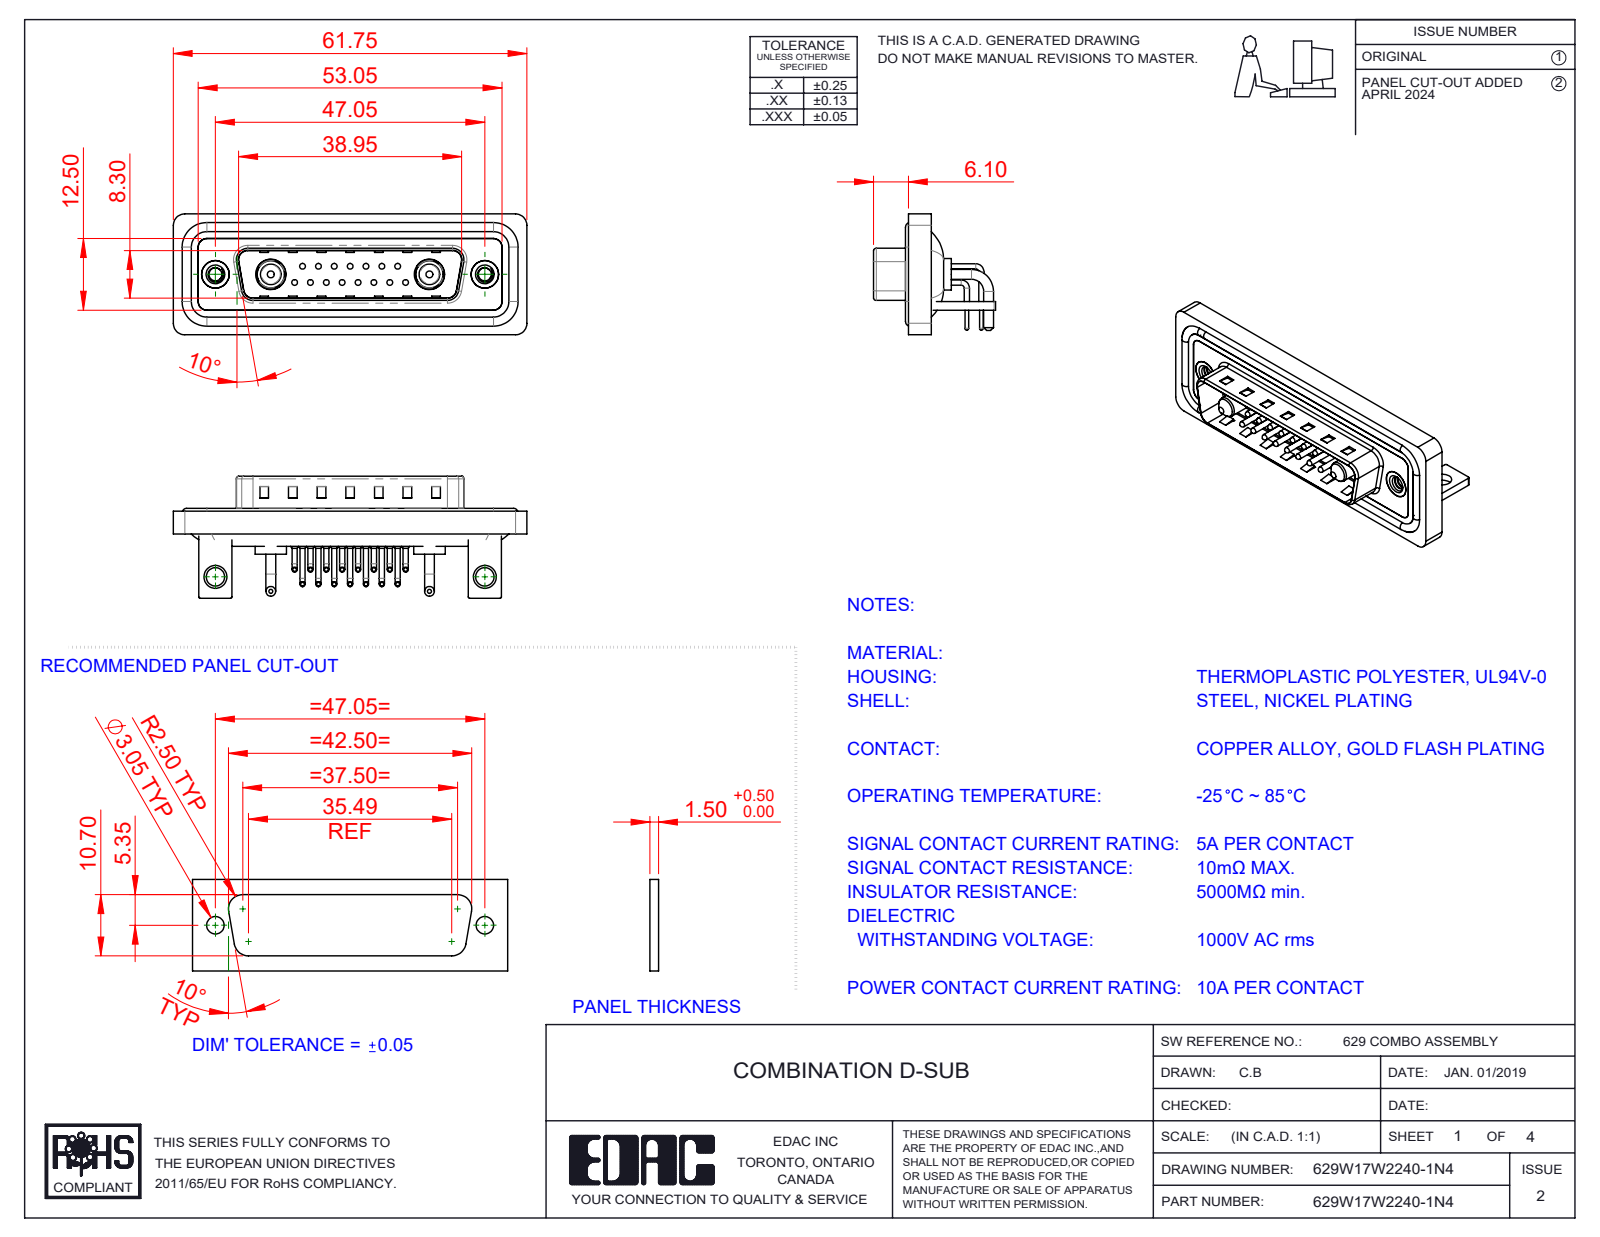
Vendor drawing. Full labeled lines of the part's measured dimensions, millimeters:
Part name (STEP PRODUCT): 629Combo Waterproof Housing_25 Contacts; 629W17W2140-1N4; 629Combo Contact Row 2; Power Pin_10A RA (+6 more)
STEP written by: SolidWorks 2023 (CONFIG_CONTROL_DESIGN)
Units: millimetres
Bodies: 28 solids, 2259 faces (1209 planar, 788 cylindrical, 262 other)
Overall size (bounding box): 61.75 × 21.3 × 21.1
Volume: 7 674 mm³ · Surface area: 13 086 mm²
Round holes (diameter × count): ⌀0.75 ×15, ⌀1.6 ×15, ⌀2 ×15, ⌀2.26 ×2, ⌀3.2 ×2, ⌀4 ×2, ⌀4.8 ×2, ⌀4.85 ×2, ⌀5 ×2, ⌀5.3 ×2
Round bosses / shafts (diameter × count): ⌀0.9 ×30, ⌀1.5 ×15, ⌀1 ×15, ⌀0.65 ×15, ⌀1.7 ×4, ⌀1.6 ×4, ⌀5.5 ×2, ⌀5.2 ×2
Partial cylindrical surfaces — rounded edges, fillets, slot ends (radius × count): R2 ×19, R1.5 ×18, R0.25 ×16, R1.01 ×15, R0.5 ×9, R1.6 ×8, R0.6 ×4, R0.65 ×4
Main face-to-face distances: 0.4, 0.8, 1.5, 2.1, 2.9, 1.1, 4.1, 1.6, 4.5, 3.7
Hole centre spacings: 3.16, 2.77, 5.54, 8.31, 5.04, 7.49, 11.08, 5.03
